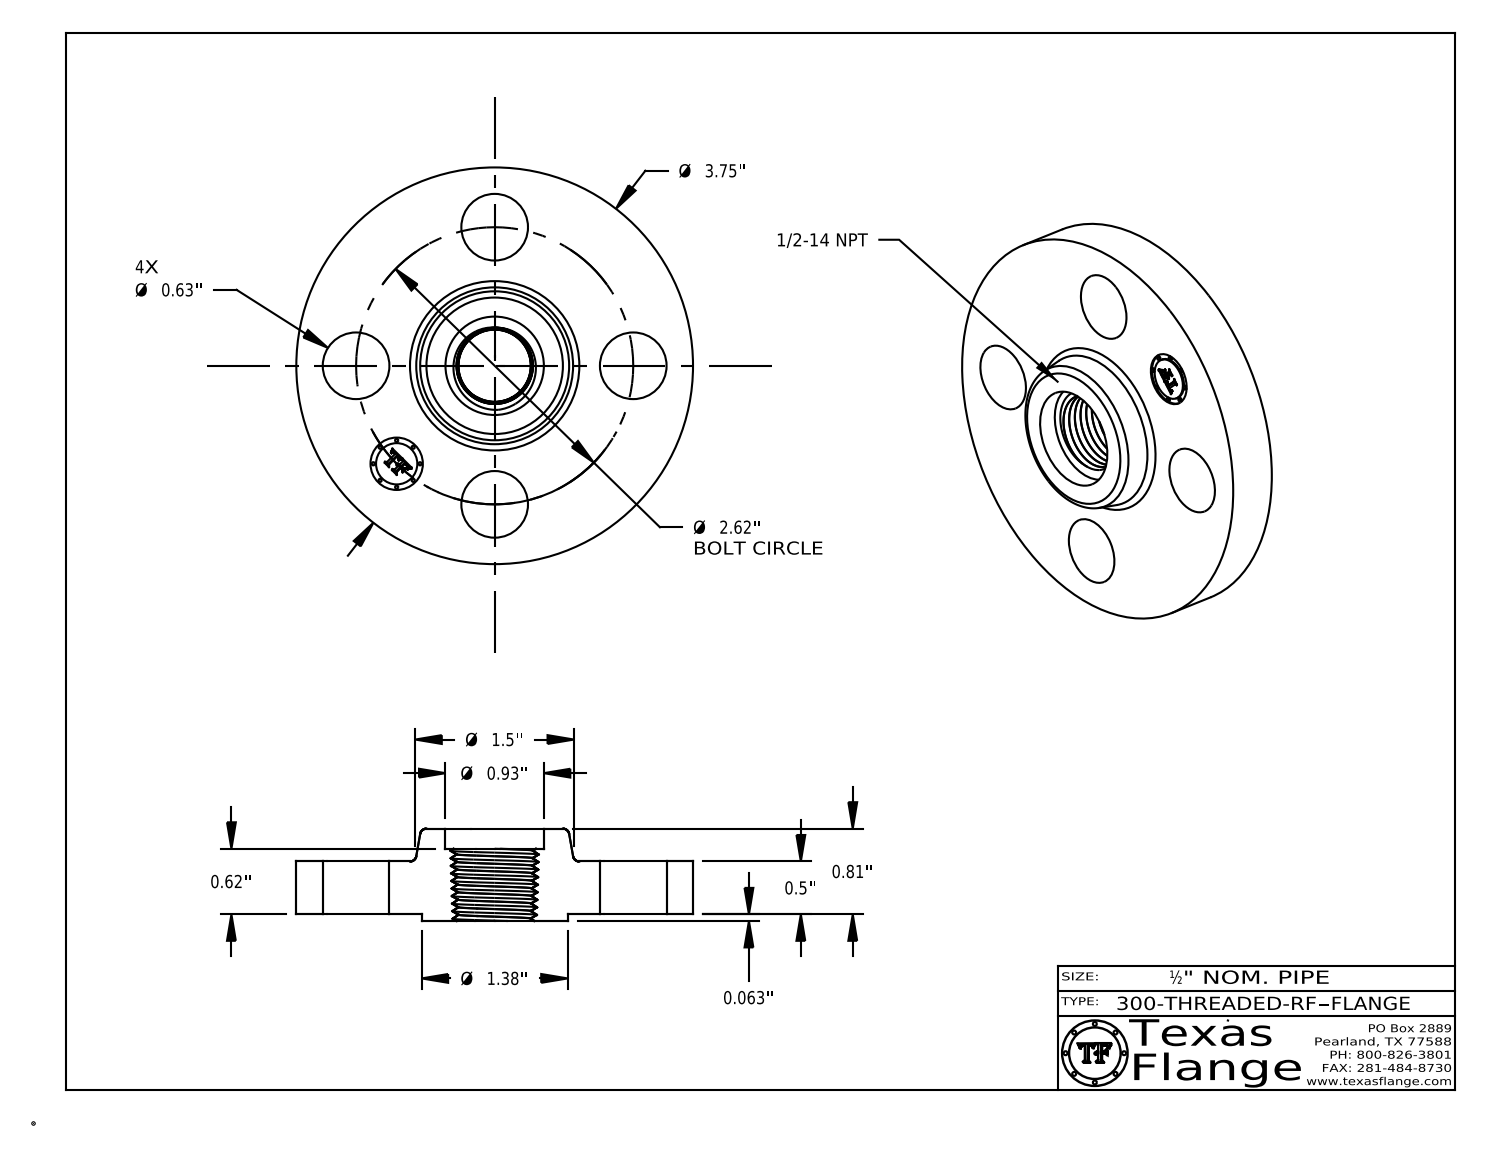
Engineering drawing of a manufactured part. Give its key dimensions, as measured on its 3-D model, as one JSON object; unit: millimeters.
{"part_name": "300-THREADED-RF", "step_written_by": "CATIA V5 STEP AP214 (AUTOMOTIVE_DESIGN)", "units": "millimeters", "bodies": {"solids": 1, "faces": 513, "planar": 370, "cylindrical": 34, "other": 109}, "overall_size": [95.3, 95.3, 22.2], "volume_mm3": 82970, "surface_area_mm2": 21630, "round_holes": [[16, 4], [12.6, 1], [23.6, 1]], "round_bosses_or_shafts": [[0.8, 8], [95.3, 1], [35.1, 1], [9.9, 1]], "face_to_face_distances": [12.7, 1.6, 14.3, 22.1, 20.6, 7.9, 17.3, 15.7, 3, 4.8], "hole_center_spacings": [33.3, 47, 25.5, 61.5, 66.5, 33.3]}
